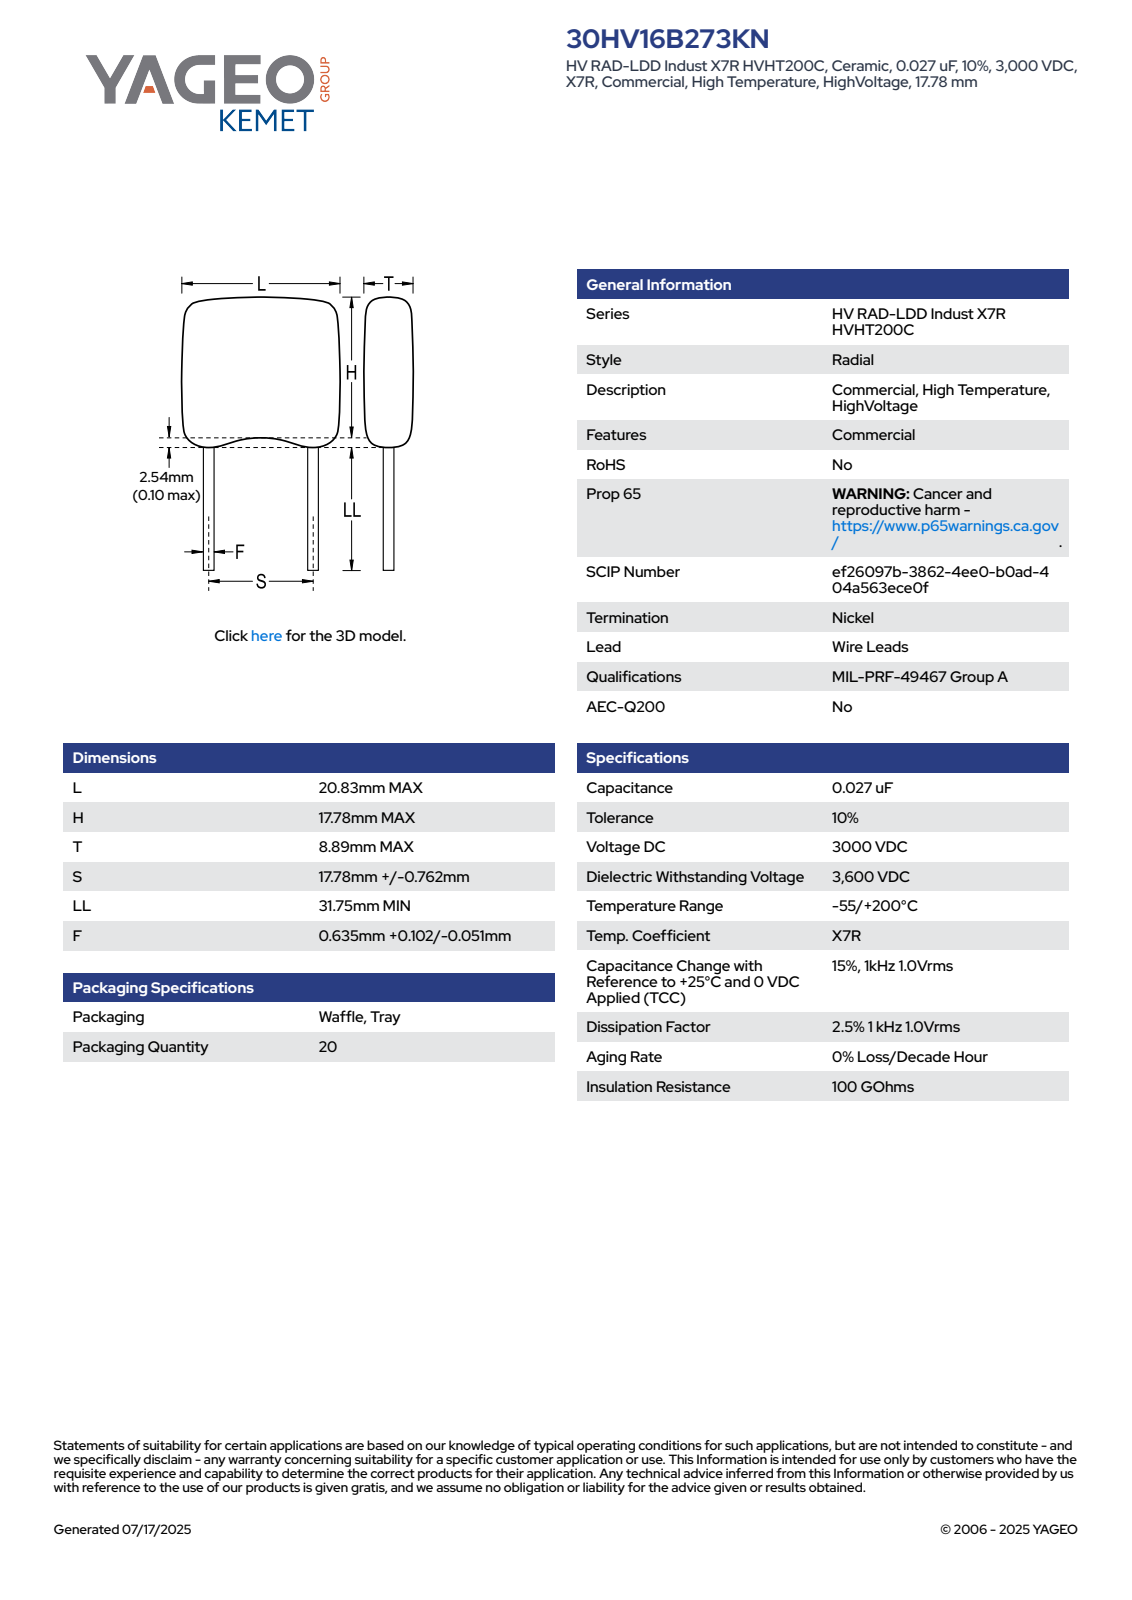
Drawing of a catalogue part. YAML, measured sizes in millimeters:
part_name: "CCRM_RCST_HV16_L20.83H17.78T8.89S17.78LL3.175F0.737"
step_written_by: "SolidWorks 2021 (AUTOMOTIVE_DESIGN)"
units: millimeters
bodies: {solids: 4, faces: 92, planar: 66, cylindrical: 16, other: 10}
overall_size: [51.05, 20.83, 5.08]
volume: 1918
surface_area: 1293
round_bosses_or_shafts:
  - {diameter: 0.64, count: 2}
partial_cylinders:
  - {radius: 0.5, count: 8}
  - {radius: 2, count: 4}
face_to_face_distances: [5.08, 20.83, 19.3, 31.75, 51.05, 43.34, 11.59, 7.71, 40.03, 8.28]
